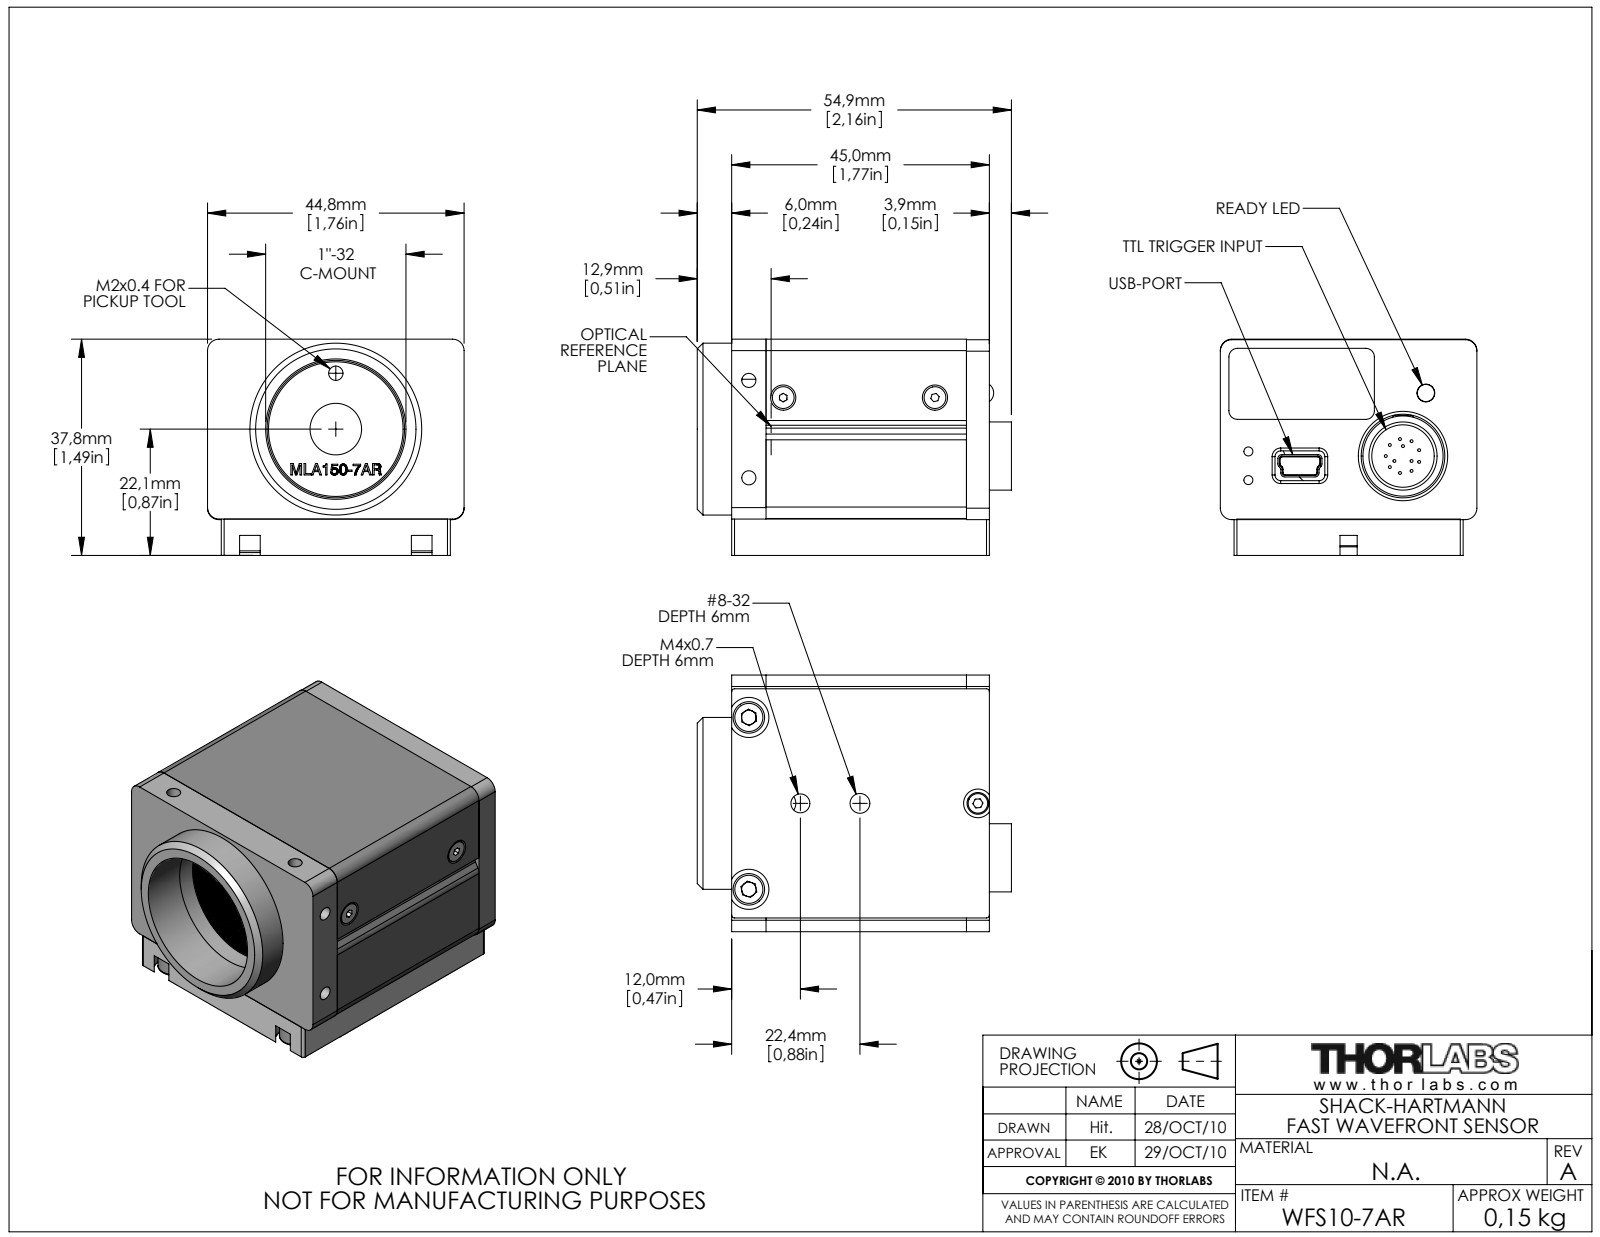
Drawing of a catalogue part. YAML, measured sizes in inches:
part_name: "21156-E0W"
step_written_by: "SolidWorks 2010 (CONFIG_CONTROL_DESIGN)"
units: inches
bodies: {solids: 0, faces: 322, planar: 161, cylindrical: 125, other: 36}
overall_size: [2.16, 1.764, 1.486]
round_holes:
  - {diameter: 0.097, count: 3}
  - {diameter: 0.097, count: 2}
  - {diameter: 0.276, count: 2}
  - {diameter: 0.062, count: 1}
  - {diameter: 0.062, count: 1}
  - {diameter: 0.098, count: 1}
  - {diameter: 0.122, count: 1}
  - {diameter: 0.13, count: 1}
  - {diameter: 0.136, count: 1}
  - {diameter: 0.197, count: 1}
  - {diameter: 0.354, count: 1}
  - {diameter: 0.429, count: 1}
round_bosses_or_shafts:
  - {diameter: 0.02, count: 12}
  - {diameter: 0.15, count: 3}
  - {diameter: 0.217, count: 2}
  - {diameter: 1.181, count: 1}
  - {diameter: 0.469, count: 1}
  - {diameter: 0.118, count: 1}
partial_cylinders:
  - {radius: 0.079, count: 12}
  - {radius: 0.012, count: 8}
  - {radius: 0.039, count: 6}
  - {radius: 0.02, count: 4}
  - {radius: 0.028, count: 4}
  - {radius: 0.059, count: 4}
face_to_face_distances: [1.486, 1.232, 0.254, 1.764, 1.487, 1.772, 0.285, 0.094, 1.669, 0.039]
hole_center_spacings: [0.689, 0.965, 1.682, 0.197, 0.384, 0.409, 0.417, 0.461]
